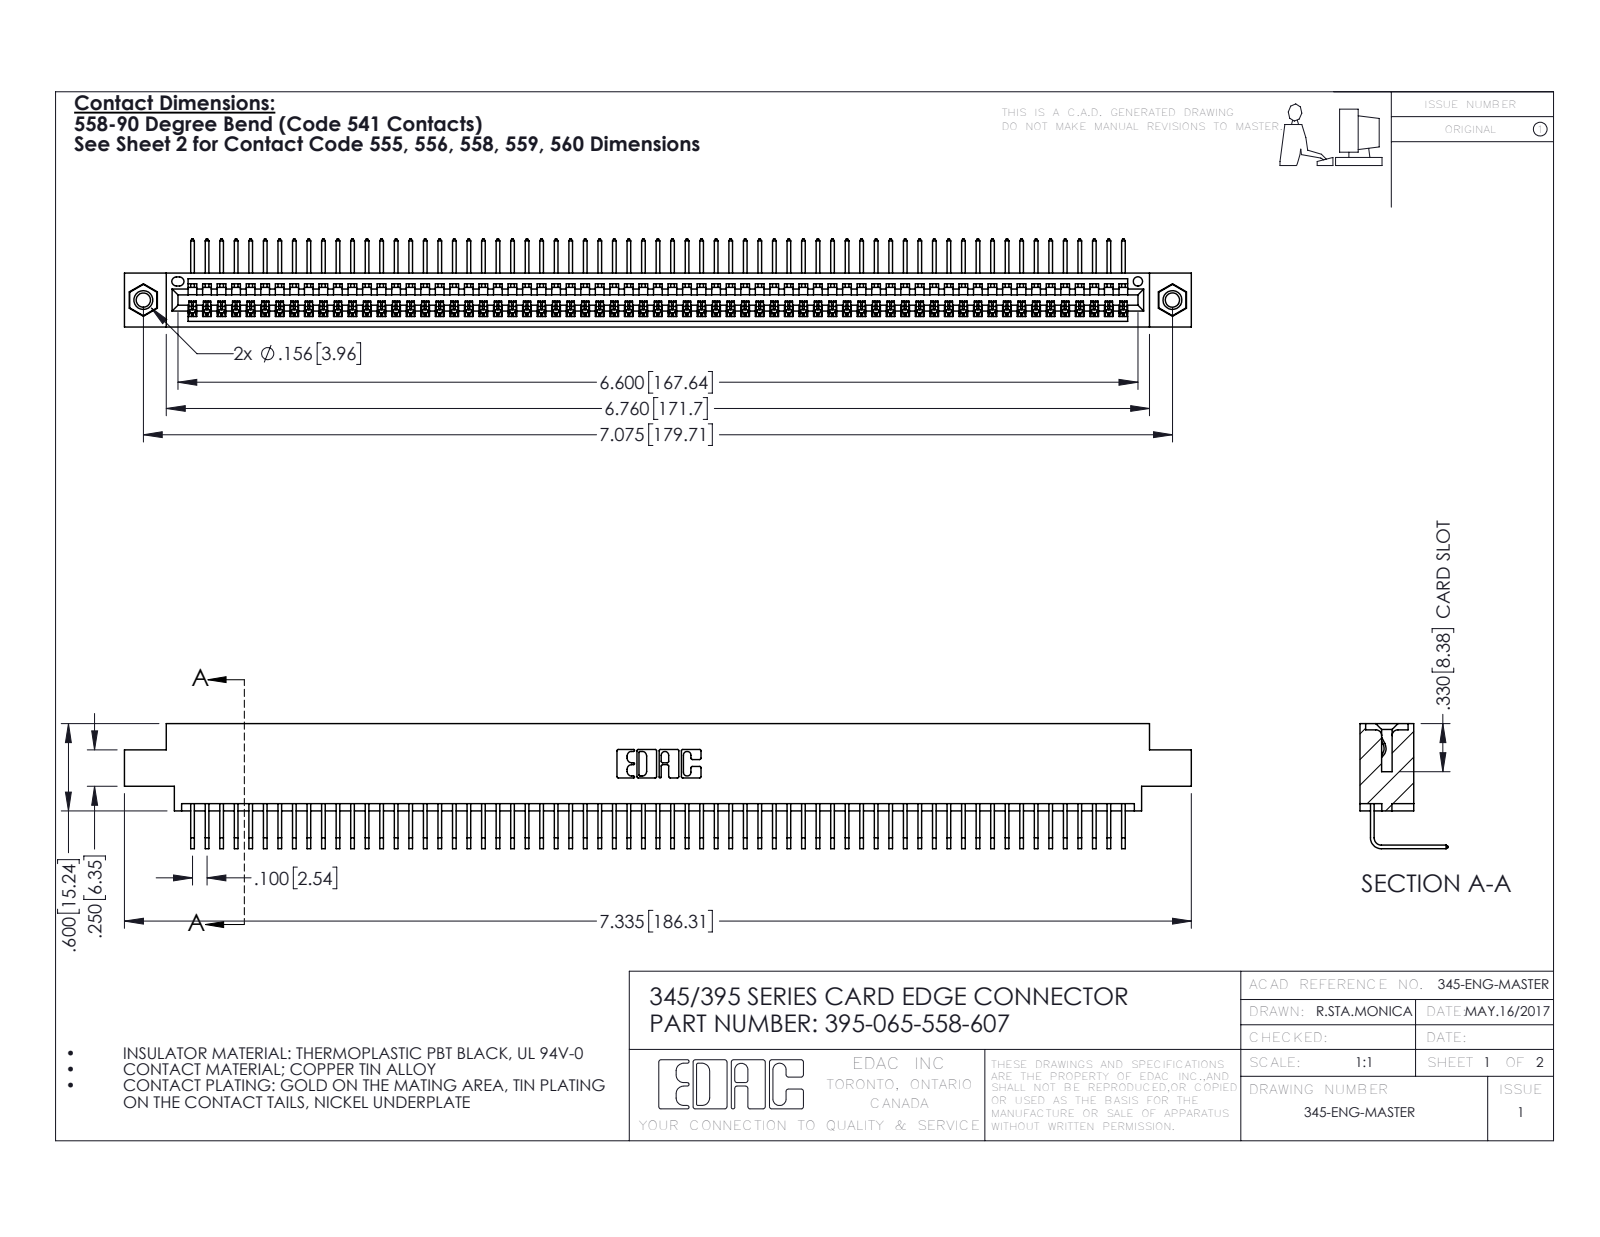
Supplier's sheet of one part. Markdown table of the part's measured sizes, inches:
| quantity | value |
| --- | --- |
| part name | 345-292-001_558 Tail - 2; 395-065-558-607; 345 Part_0.170 Offset - 0.156 Dia-TI; 345-250-001_345-250-005-103 |
| STEP written by | SolidWorks 2016 (CONFIG_CONTROL_DESIGN) |
| units | inches |
| bodies | 68 solids, 4090 faces (2846 planar, 1228 cylindrical, 16 other) |
| overall size | 7.335 × 0.859 × 0.605 |
| volume | 1.097 in³ |
| surface area | 39.73 in² |
| round holes (diameter × count) | 0.098 × 2, 0.125 × 2, 0.156 × 2, 0.064 × 1 |
| round bosses / shafts (diameter × count) | 0.155 × 2 |
| partial cylindrical surfaces (radius × count) | 0.006 × 130, 0.01 × 22, 0.007 × 6, 0.031 × 6, 0.026 × 3, 0.031 × 2, 0.04 × 2, 0.014 × 1 |
| main face-to-face distances | 0.072, 0.298, 0.37, 0.2, 0.098, 0.272, 0.025, 0.225, 0.175, 0.149 |
| hole center spacings | 0.27, 6.839, 7.075 |
